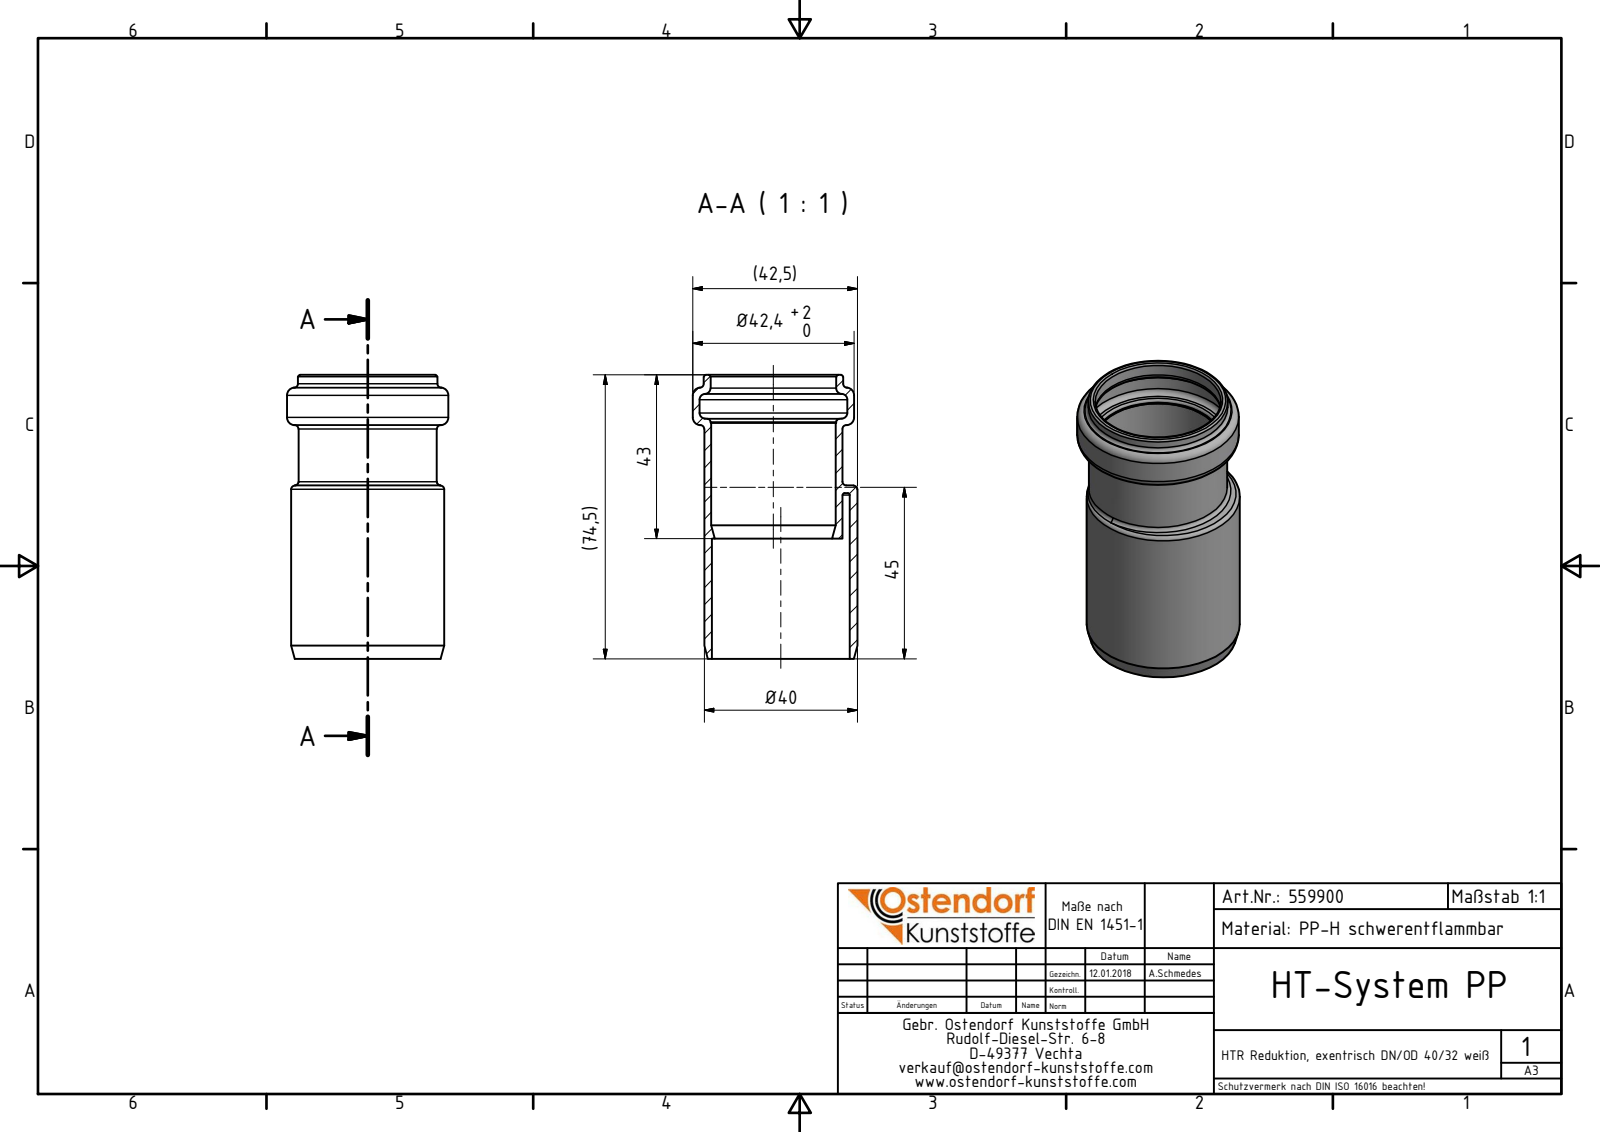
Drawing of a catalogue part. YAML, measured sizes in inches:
part_name: "559900 HTR DN_OD 40_32 weiß"
step_written_by: "Autodesk Inventor 2016 (AUTOMOTIVE_DESIGN)"
units: inches
bodies: {solids: 1, faces: 38, planar: 6, cylindrical: 10, other: 22}
overall_size: [2.934, 1.703, 1.669]
volume: 1.201
surface_area: 31.35
round_holes:
  - {diameter: 1.287, count: 1}
  - {diameter: 1.299, count: 1}
  - {diameter: 1.425, count: 1}
  - {diameter: 1.528, count: 1}
round_bosses_or_shafts:
  - {diameter: 1.669, count: 1}
  - {diameter: 1.583, count: 1}
  - {diameter: 1.441, count: 1}
  - {diameter: 1.429, count: 1}
face_to_face_distances: [1.241, 2.934, 1.693, 1.791, 0.55, 1.143, 1.713, 0.472, 0.079, 1.221]
hole_center_spacings: [0.077]
